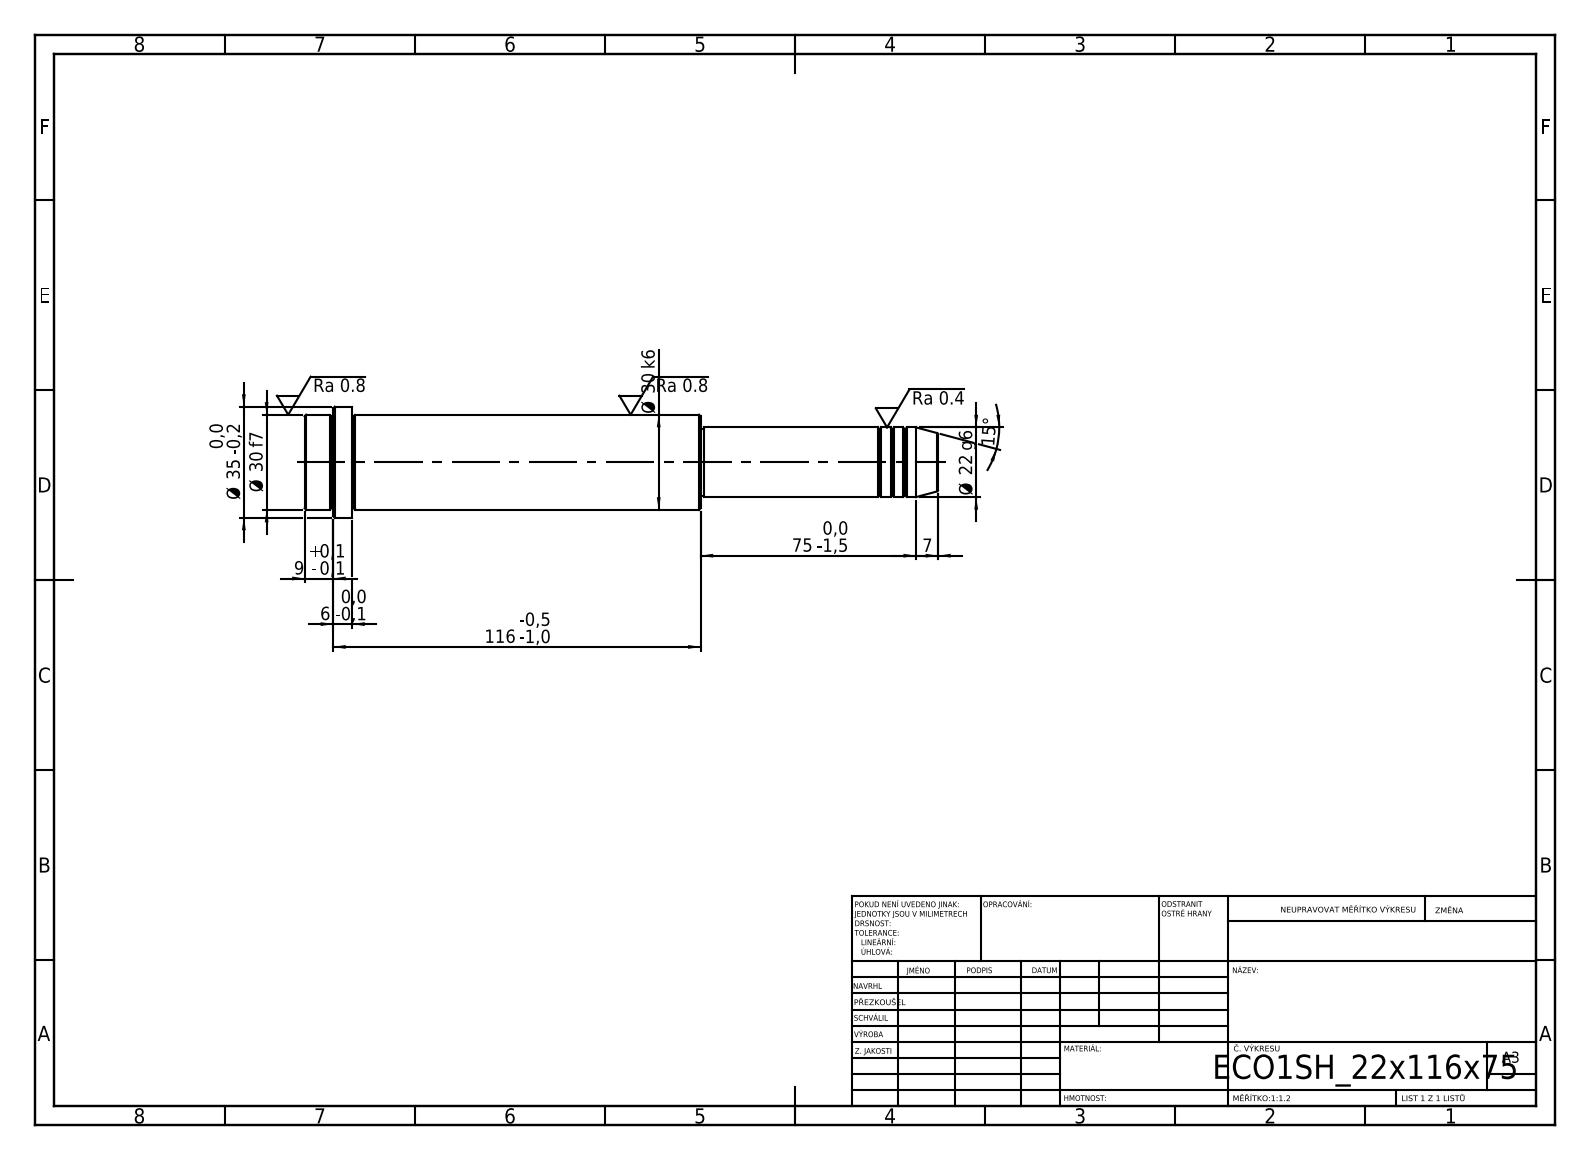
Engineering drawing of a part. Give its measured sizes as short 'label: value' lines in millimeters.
written by: SolidWorks 2019 (CONFIG_CONTROL_DESIGN)
unit: mm
bodies: 1 solid, 52 faces (6 planar, 16 cylindrical, 30 other)
size: 200 × 35 × 35
volume: 117 746 mm³; area: 19 019 mm²
bosses: 1× ⌀35, 1× ⌀30, 1× ⌀22, 1× ⌀21
face distances: 125, 110, 15, 75, 185, 200, 191, 116, 6, 9
